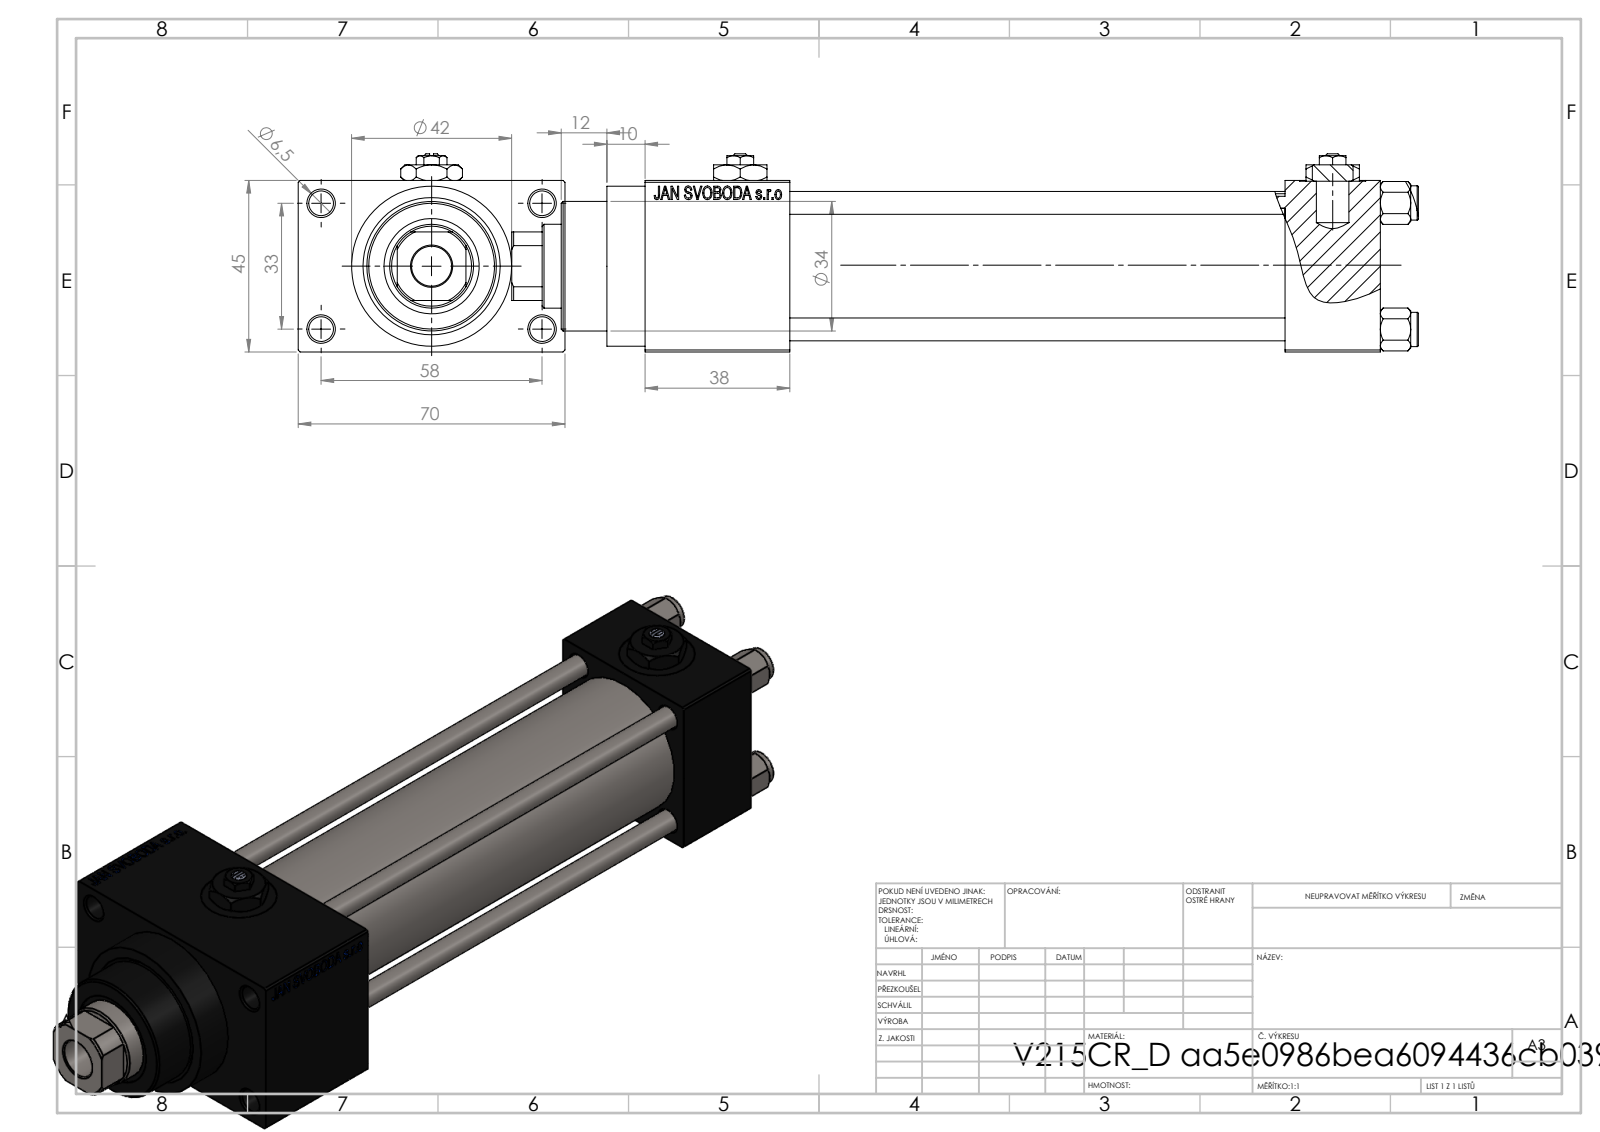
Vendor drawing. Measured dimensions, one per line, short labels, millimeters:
name: NUT_M5_D; V215CR_D_Body; V215_VC_A; V215CR_VCP_D (+2 more)
written by: SolidWorks 2019 (CONFIG_CONTROL_DESIGN)
unit: mm
bodies: 13 solids, 1203 faces (542 planar, 99 cylindrical, 562 other)
size: 238 × 70 × 52
volume: 307 472 mm³; area: 110 778 mm²
holes: 4× ⌀6, 4× ⌀6.5, 4× ⌀13.16, 4× ⌀20, 3× ⌀7, 1× ⌀10.5, 1× ⌀22, 1× ⌀24, 1× ⌀25, 1× ⌀32, 1× ⌀33
bosses: 4× ⌀9, 1× ⌀42, 1× ⌀38, 1× ⌀34
rounds: 1× R10.5
face distances: 45, 25, 12.5, 130, 155, 57.5, 168, 38, 193, 70
hole spacings: 12.4, 23.48, 33.2, 33.37, 35.35, 45.6, 56.35, 33
